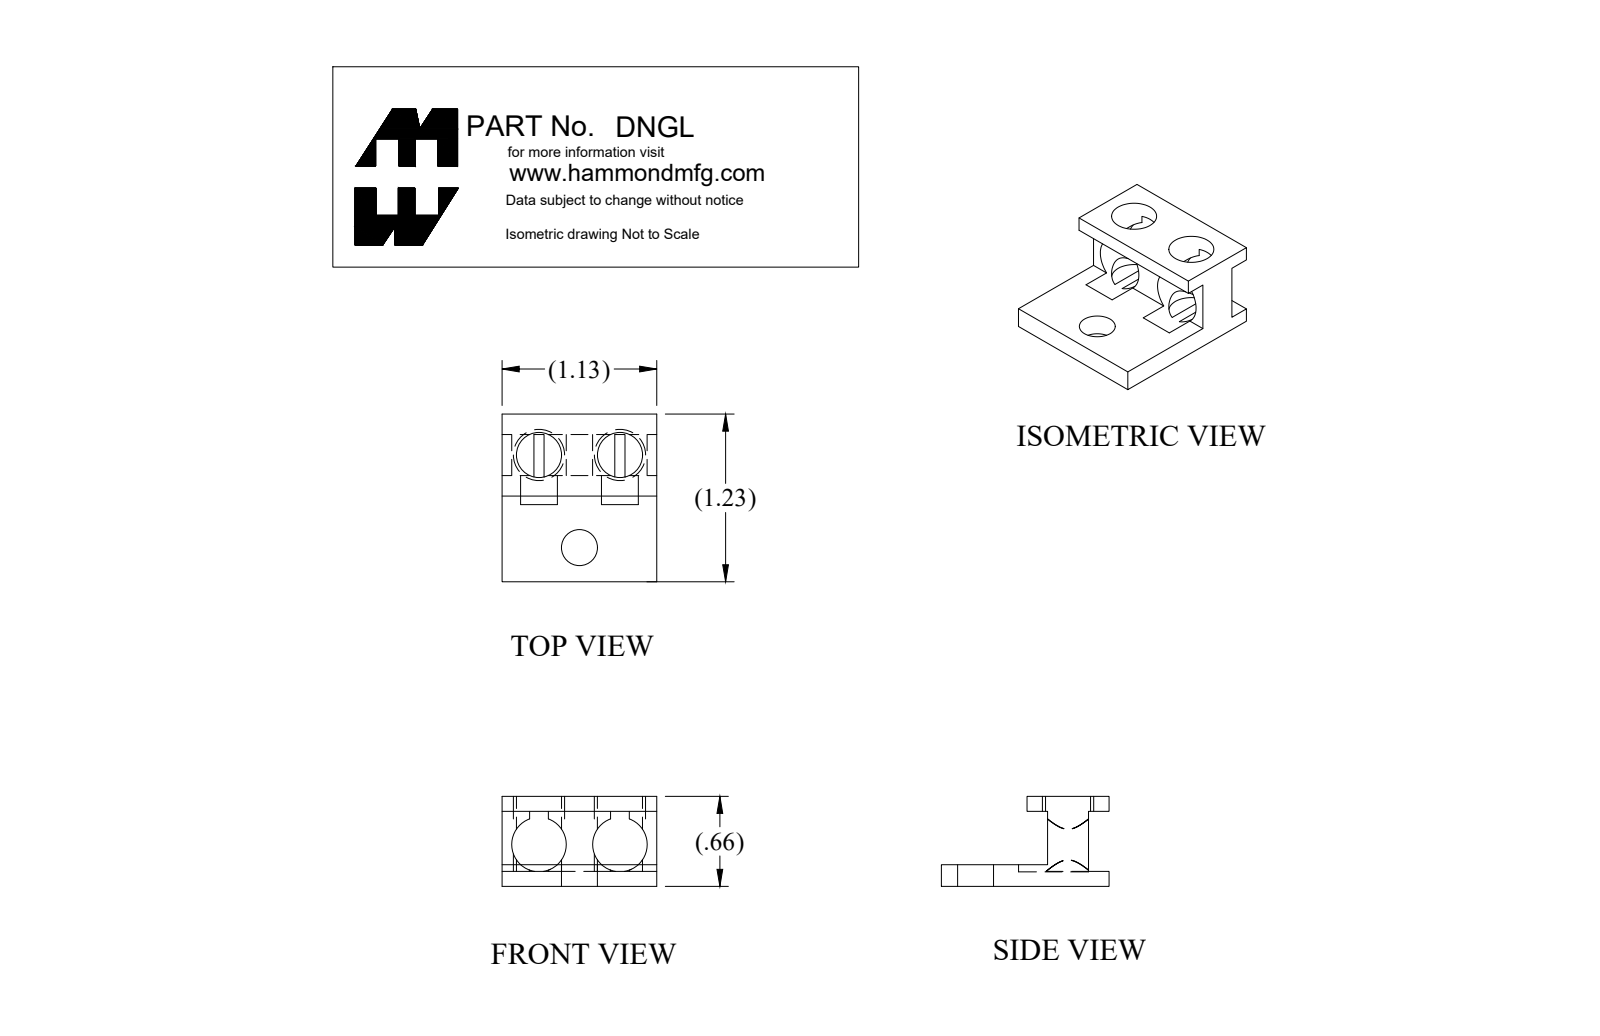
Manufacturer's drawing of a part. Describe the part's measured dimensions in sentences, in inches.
The part is named "DNGL_Default". Its 3-D file was written by "SolidWorks 2018 (CONFIG_CONTROL_DESIGN)". It is 1 solid with 36 faces: 22 planar, 14 cylindrical and 0 other. Overall it measures 1.227 by 1.132 by 0.659 inches. Its volume is 0.3 cubic inches and its surface area 6.059 square inches. Round holes: 2 of diameter 0.33, 2 of diameter 0.399, 1 of diameter 0.263. The main face-to-face distances are 0.159, 0.659, 0.5, 1.132, 0.15, 0.549, 0.39, 0.11, 0.45, 0.11. The hole center spacings are 0.592, 0.593, 0.739, 0.739.
